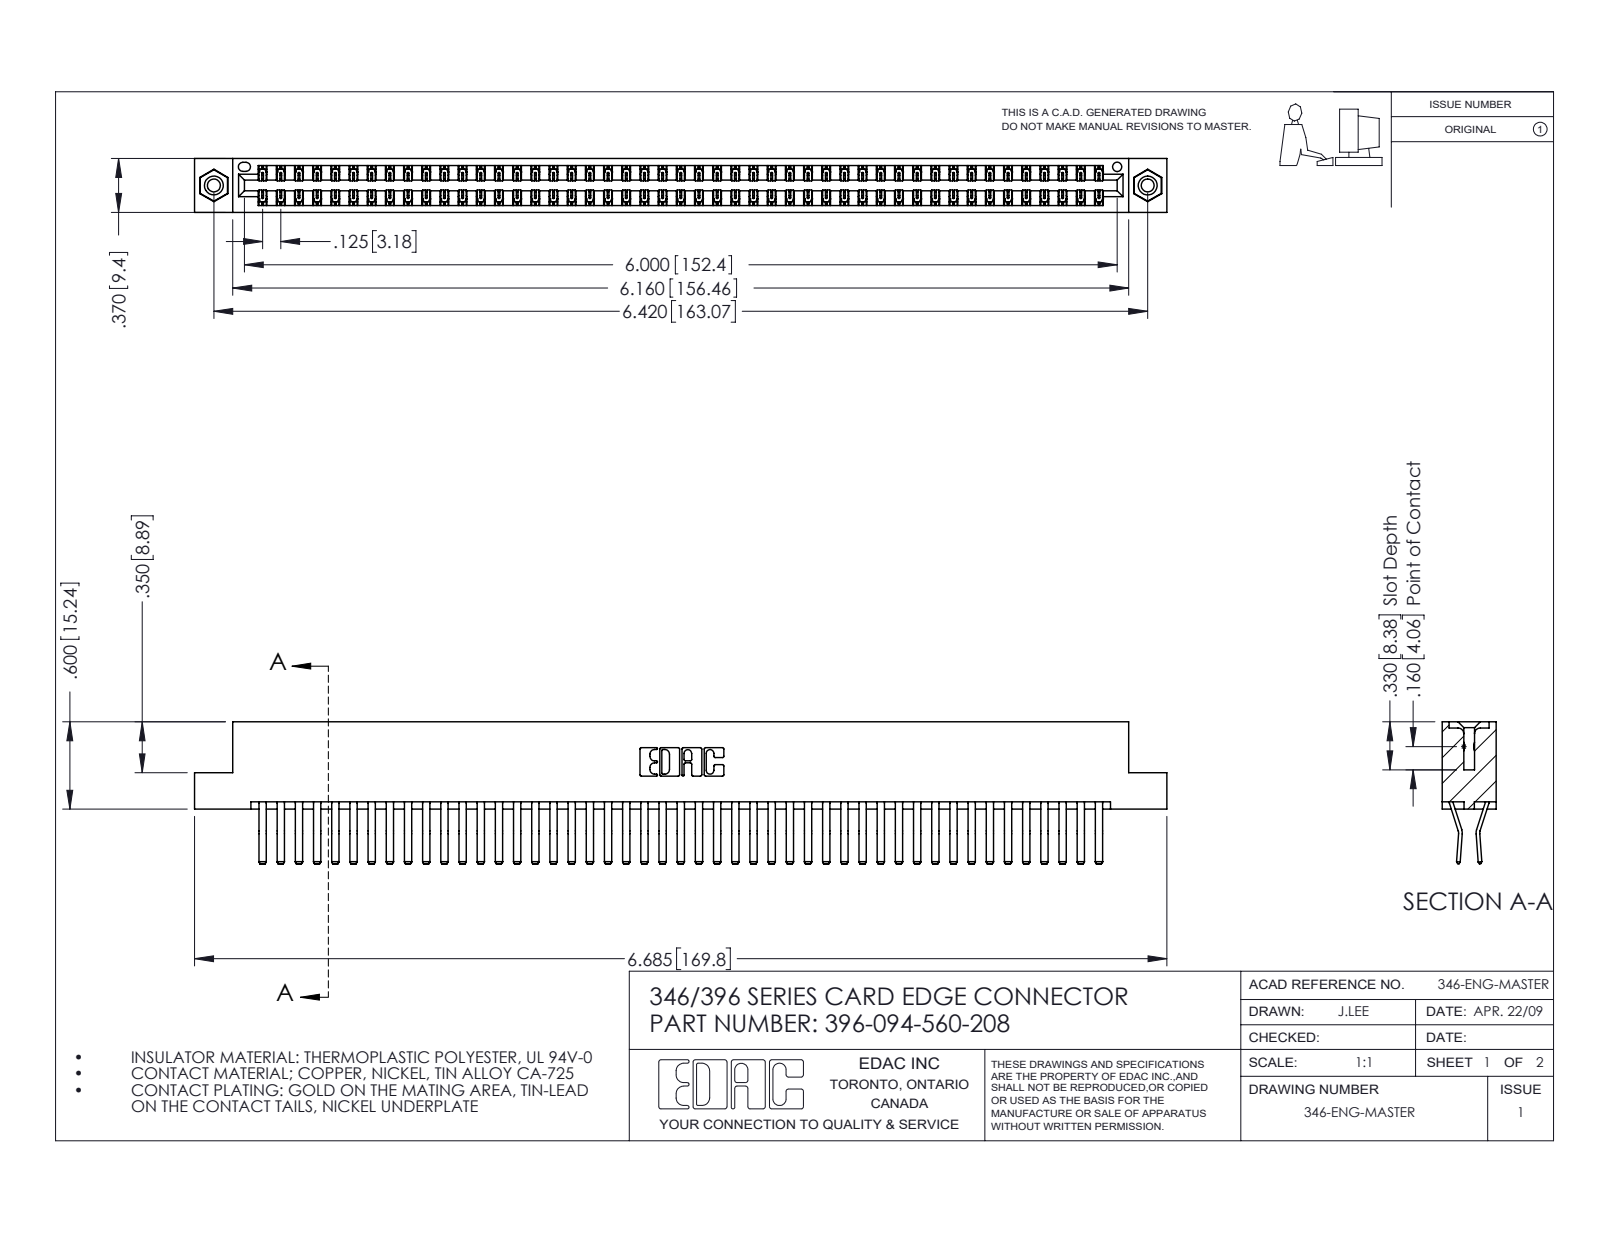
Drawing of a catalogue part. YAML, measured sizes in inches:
part_name: "345-250-001_345-250-003-102; 345-292-001_560 Tail; 346 Part_Flush Mounting Lugs - 0.156 Dia-TI; 396-094-560-208"
step_written_by: "SolidWorks 2016 (CONFIG_CONTROL_DESIGN)"
units: inches
bodies: {solids: 97, faces: 5258, planar: 3398, cylindrical: 1844, other: 16}
overall_size: [6.685, 0.975, 0.37]
volume: 1.05
surface_area: 39.36
round_holes:
  - {diameter: 0.089, count: 2}
  - {diameter: 0.125, count: 2}
  - {diameter: 0.156, count: 2}
  - {diameter: 0.064, count: 1}
round_bosses_or_shafts:
  - {diameter: 0.155, count: 2}
partial_cylinders:
  - {radius: 0.006, count: 141}
  - {radius: 0.01, count: 22}
  - {radius: 0.007, count: 6}
  - {radius: 0.031, count: 6}
  - {radius: 0.026, count: 3}
  - {radius: 0.01, count: 2}
  - {radius: 0.014, count: 2}
  - {radius: 0.022, count: 2}
face_to_face_distances: [0.048, 0.322, 0.37, 0.025, 0.25, 0.072, 0.298, 0.275, 0.148, 0.222]
hole_center_spacings: [0.246, 6.211, 6.42]
